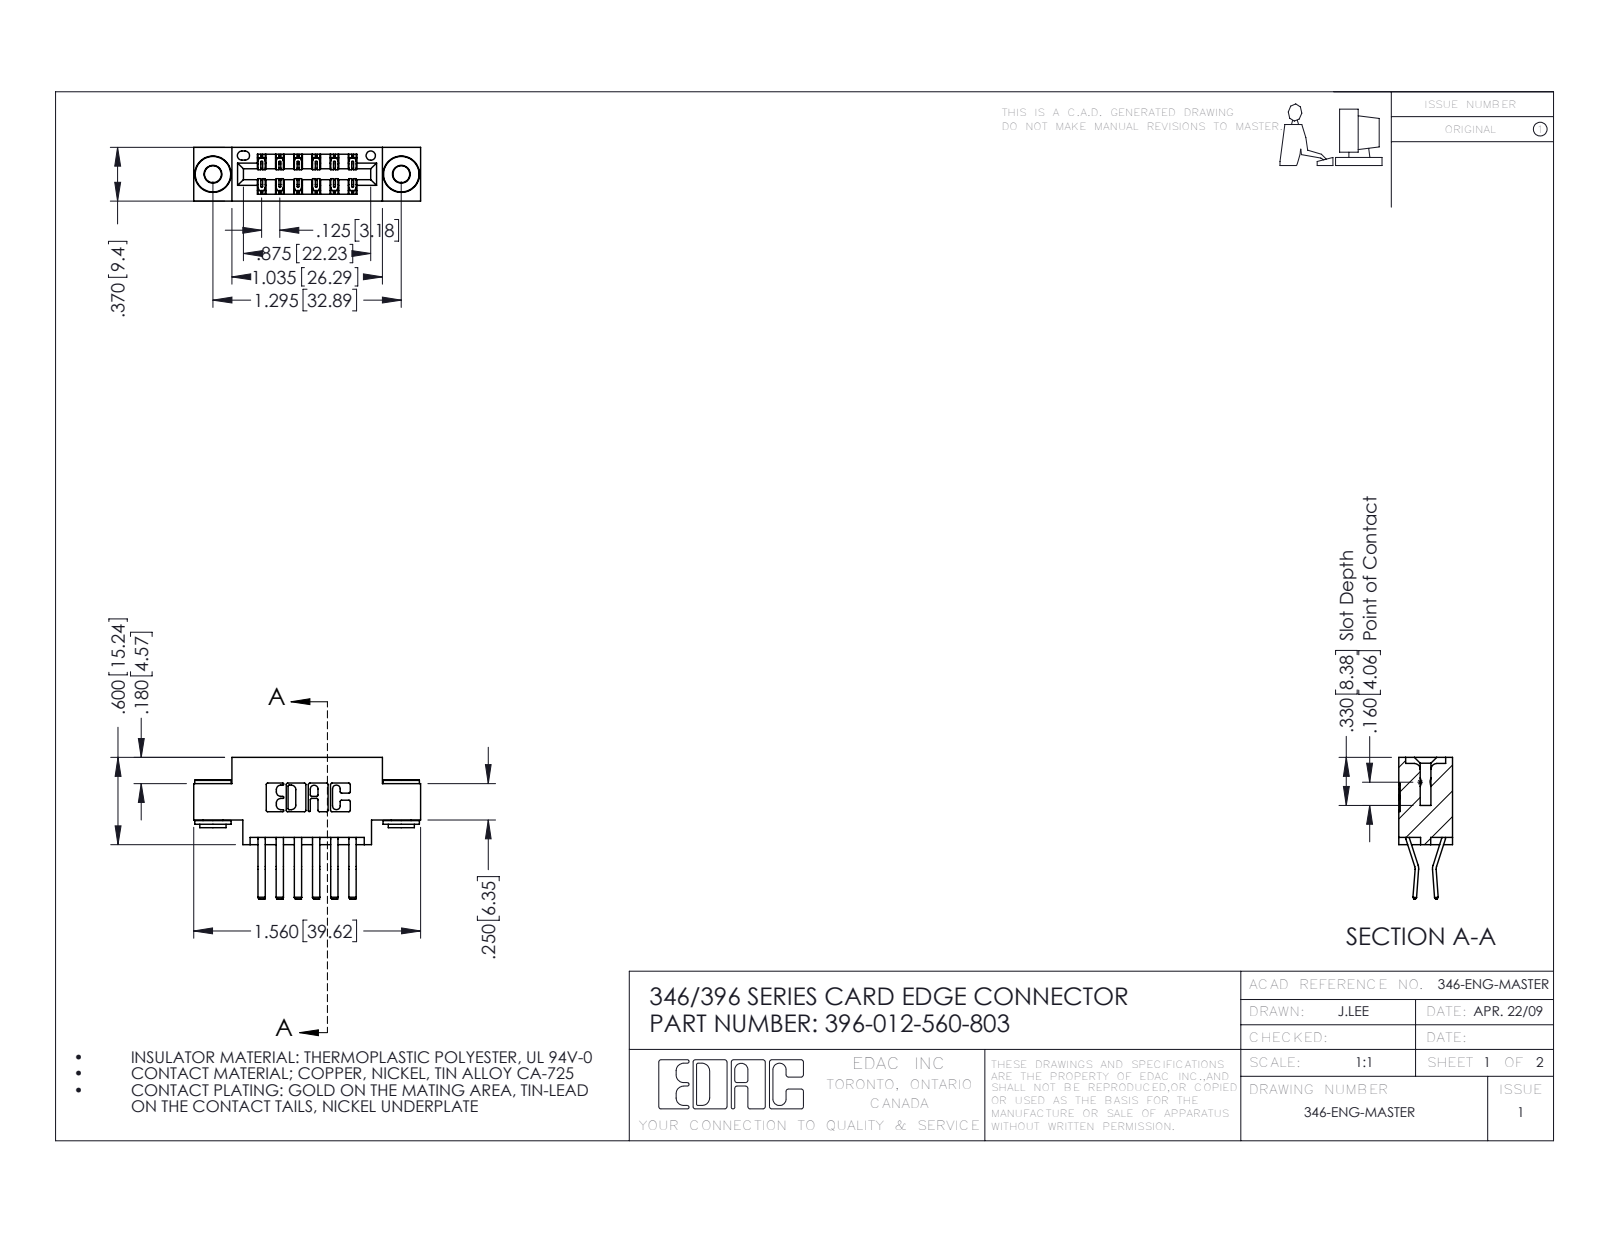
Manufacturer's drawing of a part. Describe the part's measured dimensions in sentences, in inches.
The part is named "345-292-001_560 Tail; 346 Part_0.170 Offset - 0.156 Dia-TH; 345-250-002_345-250-002-102; 396-012-560-803". Its 3-D file was written by "SolidWorks 2016 (CONFIG_CONTROL_DESIGN)". It is 15 solids with 812 faces: 510 planar, 294 cylindrical and 8 other. Overall it measures 1.56 by 0.975 by 0.37 inches. Its volume is 0.215 cubic inches and its surface area 7.575 square inches. Round holes: 2 of diameter 0.116, 2 of diameter 0.156, 1 of diameter 0.064. Round bosses or shafts: 2 of diameter 0.25, 2 of diameter 0.18, 2 of diameter 0.136. Partial cylindrical surfaces (rounded edges, fillets, slot ends): 22 of radius 0.01, 18 of radius 0.006, 6 of radius 0.007, 6 of radius 0.031, 3 of radius 0.026, 2 of radius 0.01, 2 of radius 0.014, 2 of radius 0.022. The main face-to-face distances are 0.25, 0.37, 0.048, 0.322, 0.025, 0.275, 0.148, 0.222, 0.1, 0.174. The hole center spacings are 0.246, 1.092, 1.295.
